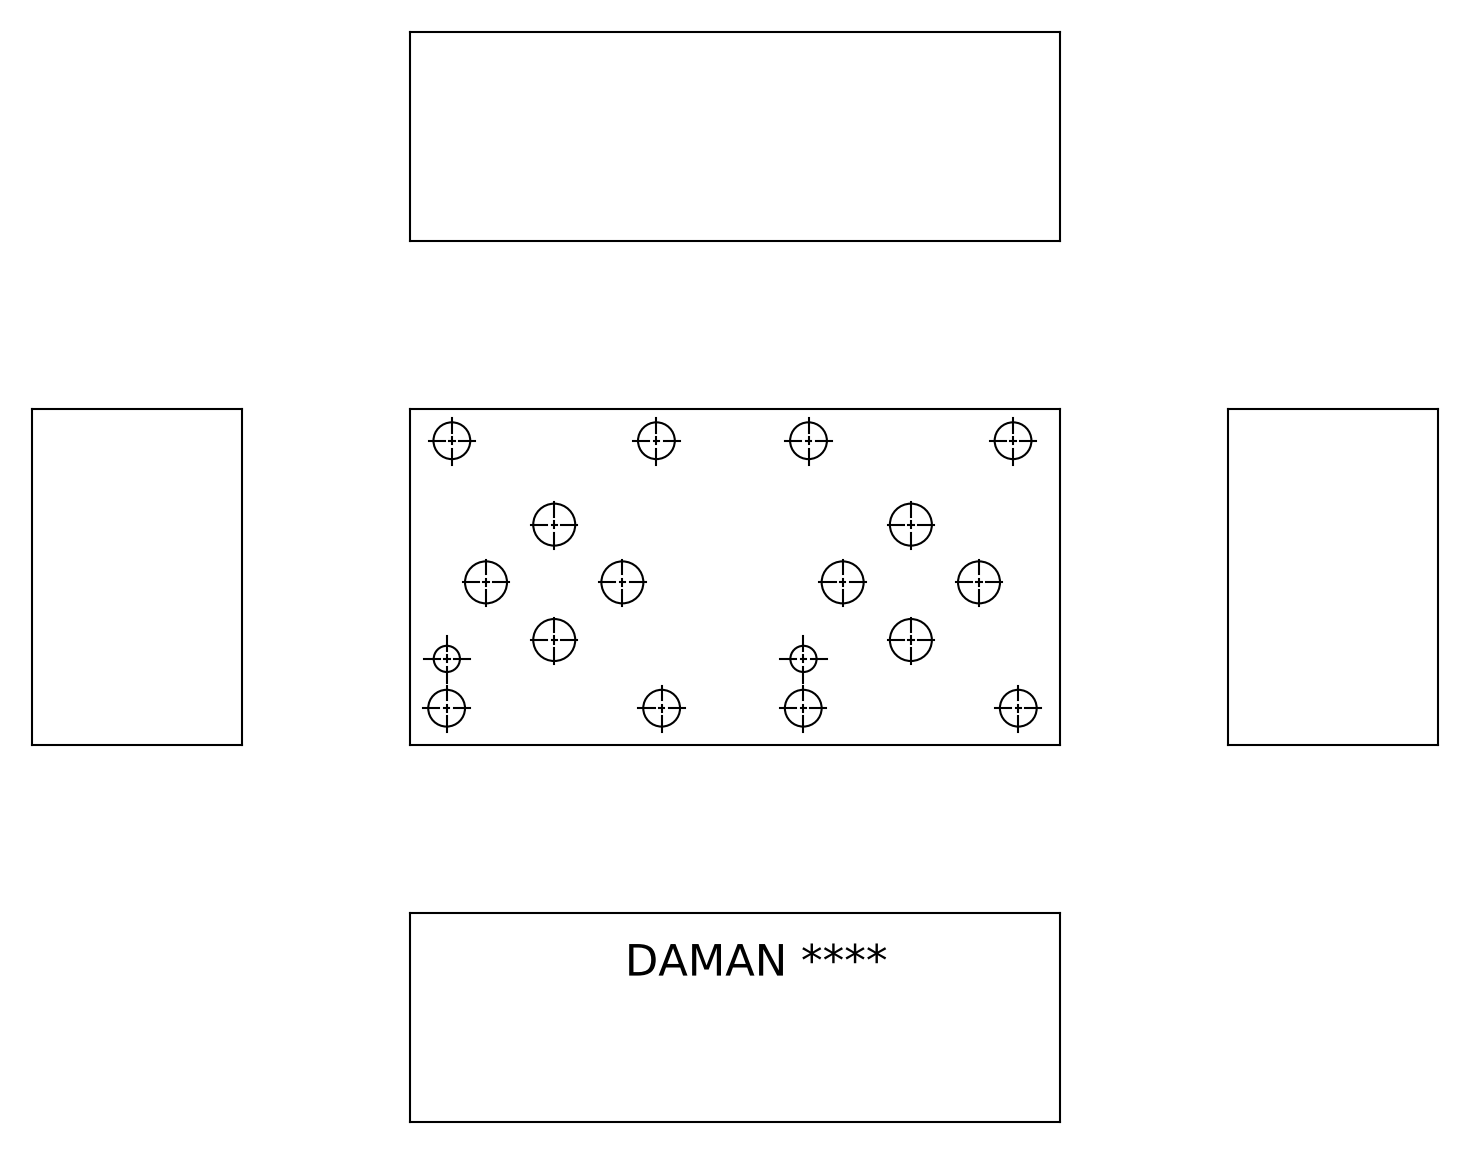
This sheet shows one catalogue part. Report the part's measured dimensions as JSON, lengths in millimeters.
{"part_name": "Part_AD03TP022AB.C08690R3_3D", "step_written_by": "Autodesk Inventor 2022 (AUTOMOTIVE_DESIGN)", "units": "millimeters", "bodies": {"solids": 1, "faces": 417, "planar": 248, "cylindrical": 41, "other": 128}, "overall_size": [98.42, 50.8, 31.75], "volume_mm3": 149710, "surface_area_mm2": 24804, "round_holes": [[7.14, 16], [5.54, 8], [12.7, 8], [3.17, 2], [3.96, 2]], "partial_cylinders_radius": [[2.77, 3]], "face_to_face_distances": [31.75, 50.8, 98.42, 1.32, 30.43, 50.76, 0.64, 7.84, 3.62, 4.83], "hole_center_spacings": [53.97, 13.52, 13.53, 20.65, 64.87, 64.9, 62.88, 53.98]}
